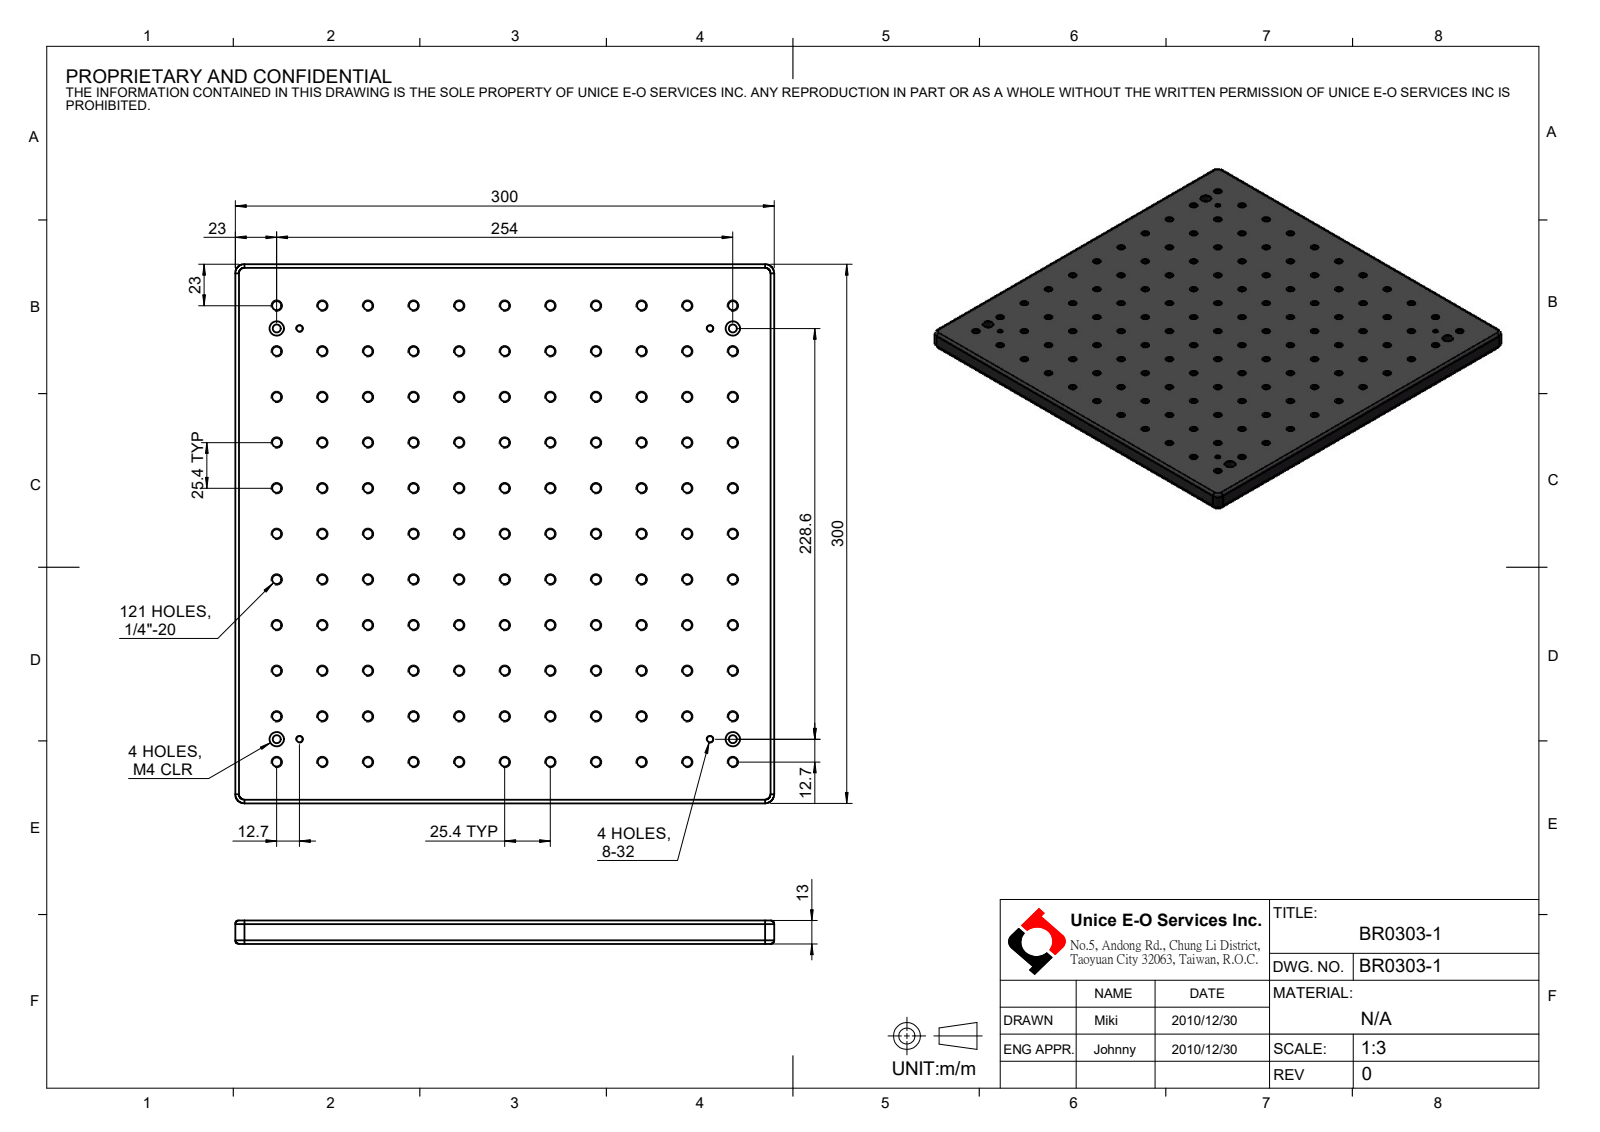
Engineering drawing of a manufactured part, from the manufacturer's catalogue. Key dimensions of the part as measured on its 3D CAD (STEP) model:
Part name (STEP PRODUCT): BR0303-1
STEP written by: SolidWorks 2016 (CONFIG_CONTROL_DESIGN)
Units: millimetres
Bodies: 1 solid, 296 faces (10 planar, 278 cylindrical, 8 other)
Overall size (bounding box): 300 × 300 × 13
Volume: 1 133 000 mm³ · Surface area: 215 033 mm²
Round holes (diameter × count): ⌀5.11 ×121, ⌀3.45 ×4, ⌀4.5 ×4, ⌀8 ×4
Partial cylindrical surfaces — rounded edges, fillets, slot ends (radius × count): R2 ×8, R5 ×4
Main face-to-face distances: 13, 300, 7, 6
Hole centre spacings: 25.4, 35.92, 50.8, 56.8, 76.2, 80.32, 101.6, 104.73
